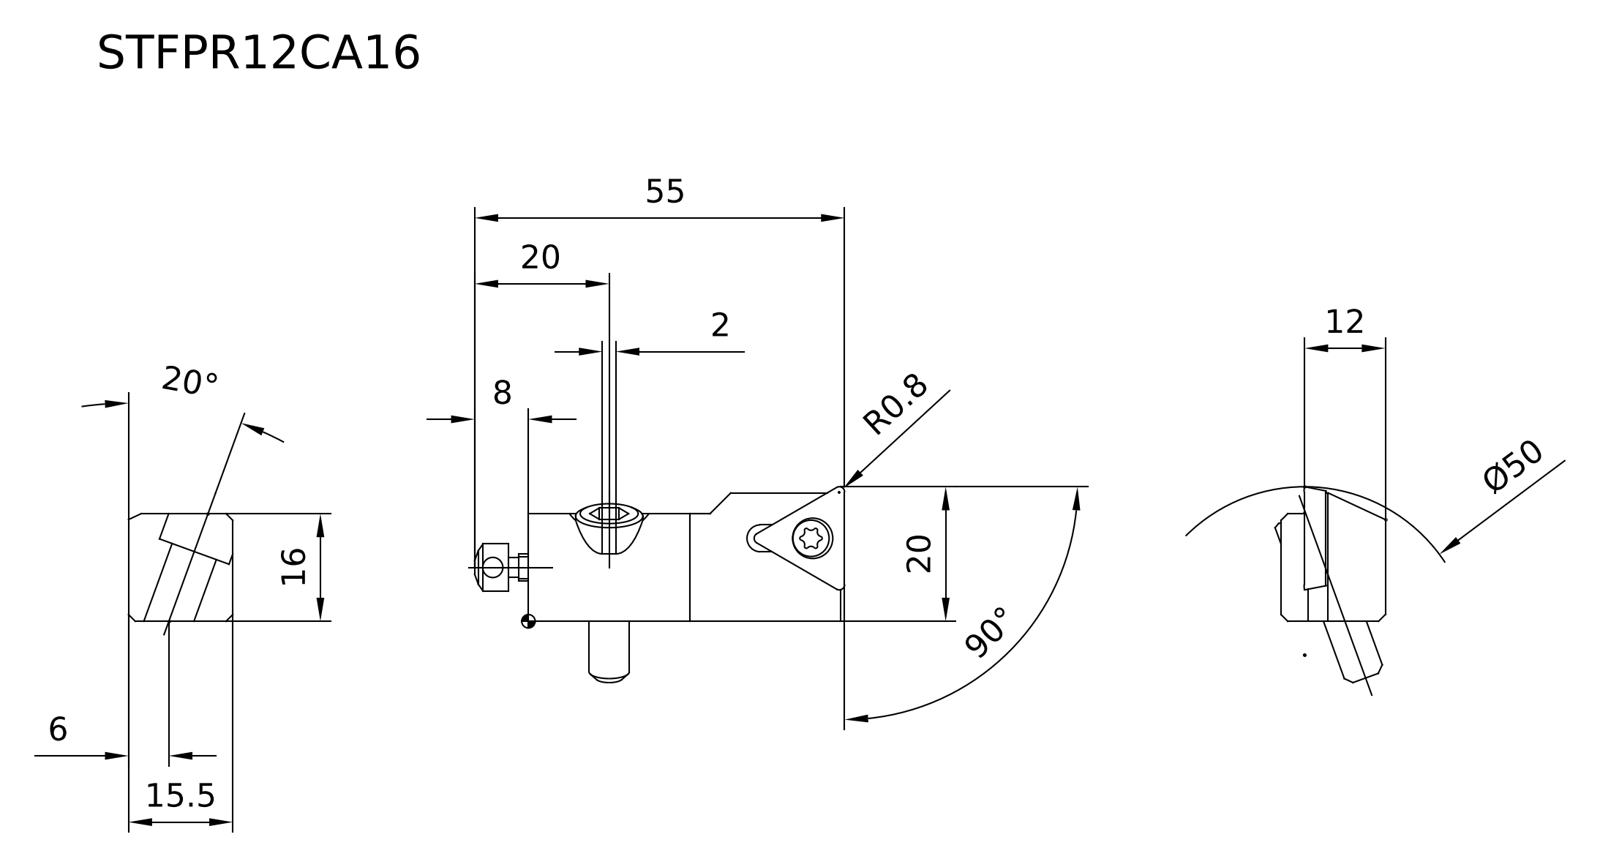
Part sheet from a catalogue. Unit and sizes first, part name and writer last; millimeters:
Units: millimetres
Overall size (bounding box): 54.36 × 28.2 × 16.39
Round holes (diameter × count): ⌀1.8 ×2, ⌀3.3 ×2, ⌀5 ×1
Round bosses / shafts (diameter × count): ⌀6 ×2, ⌀4 ×2, ⌀10 ×1, ⌀7 ×1, ⌀5.4 ×1, ⌀3 ×1
Partial cylindrical surfaces — rounded edges, fillets, slot ends (radius × count): R0.29 ×6, R0.33 ×6, R0.67 ×6, R0.84 ×6, R3.5 ×2, R5.5 ×2, R2 ×1, R10 ×1
Main face-to-face distances: 15.5, 16, 2.7, 3, 6, 3.08, 19.08, 5, 7, 8
Hole centre spacings: 41.83
Volume: 9 585 mm³ · Surface area: 5 323 mm²
Bodies: 5 solids, 141 faces (49 planar, 60 cylindrical, 32 other)
Part name (STEP PRODUCT): STFPR12CA16_ASM
STEP written by: SIEMENS PLM Software NX 10.0 (AUTOMOTIVE_DESIGN)
